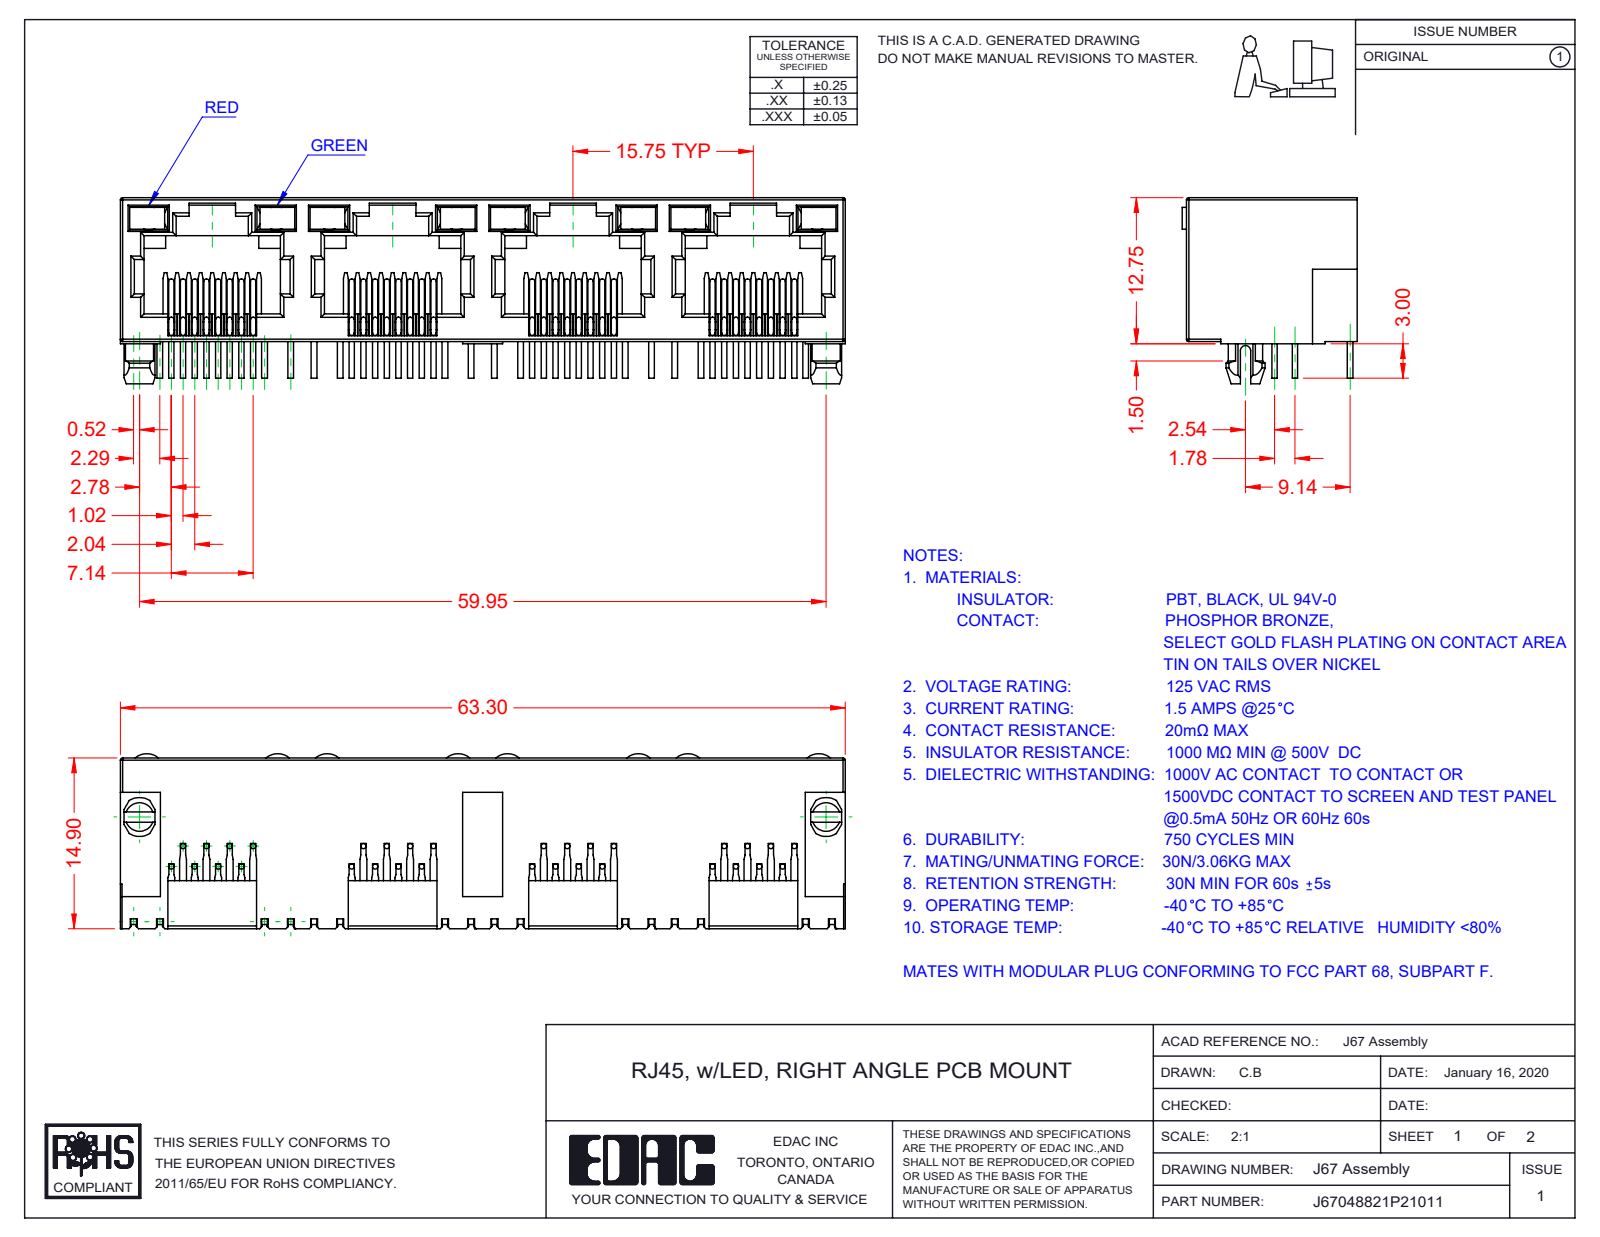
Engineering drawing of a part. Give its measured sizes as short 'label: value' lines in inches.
name: J67048822P23011; 67 Contacts; 67 Insulator; 67 LED LH_2-Red (+1 more)
written by: SolidWorks 2016 (CONFIG_CONTROL_DESIGN)
unit: in
bodies: 41 solids, 2465 faces (1781 planar, 476 cylindrical, 208 other)
size: 2.492 × 0.64 × 0.602
volume: 0.315 in³; area: 17.94 in²
bosses: 96× ⌀0.018
rounds: 66× R0.008, 29× R0.012, 9× R0.018, 8× R0.061, 2× R0.059, 2× R0.067, 1× R0.014, 1× R0.039
face distances: 0.02, 0.494, 0.074, 0.035, 0.394, 0.62, 0.039, 0.055, 0.433, 0.468
